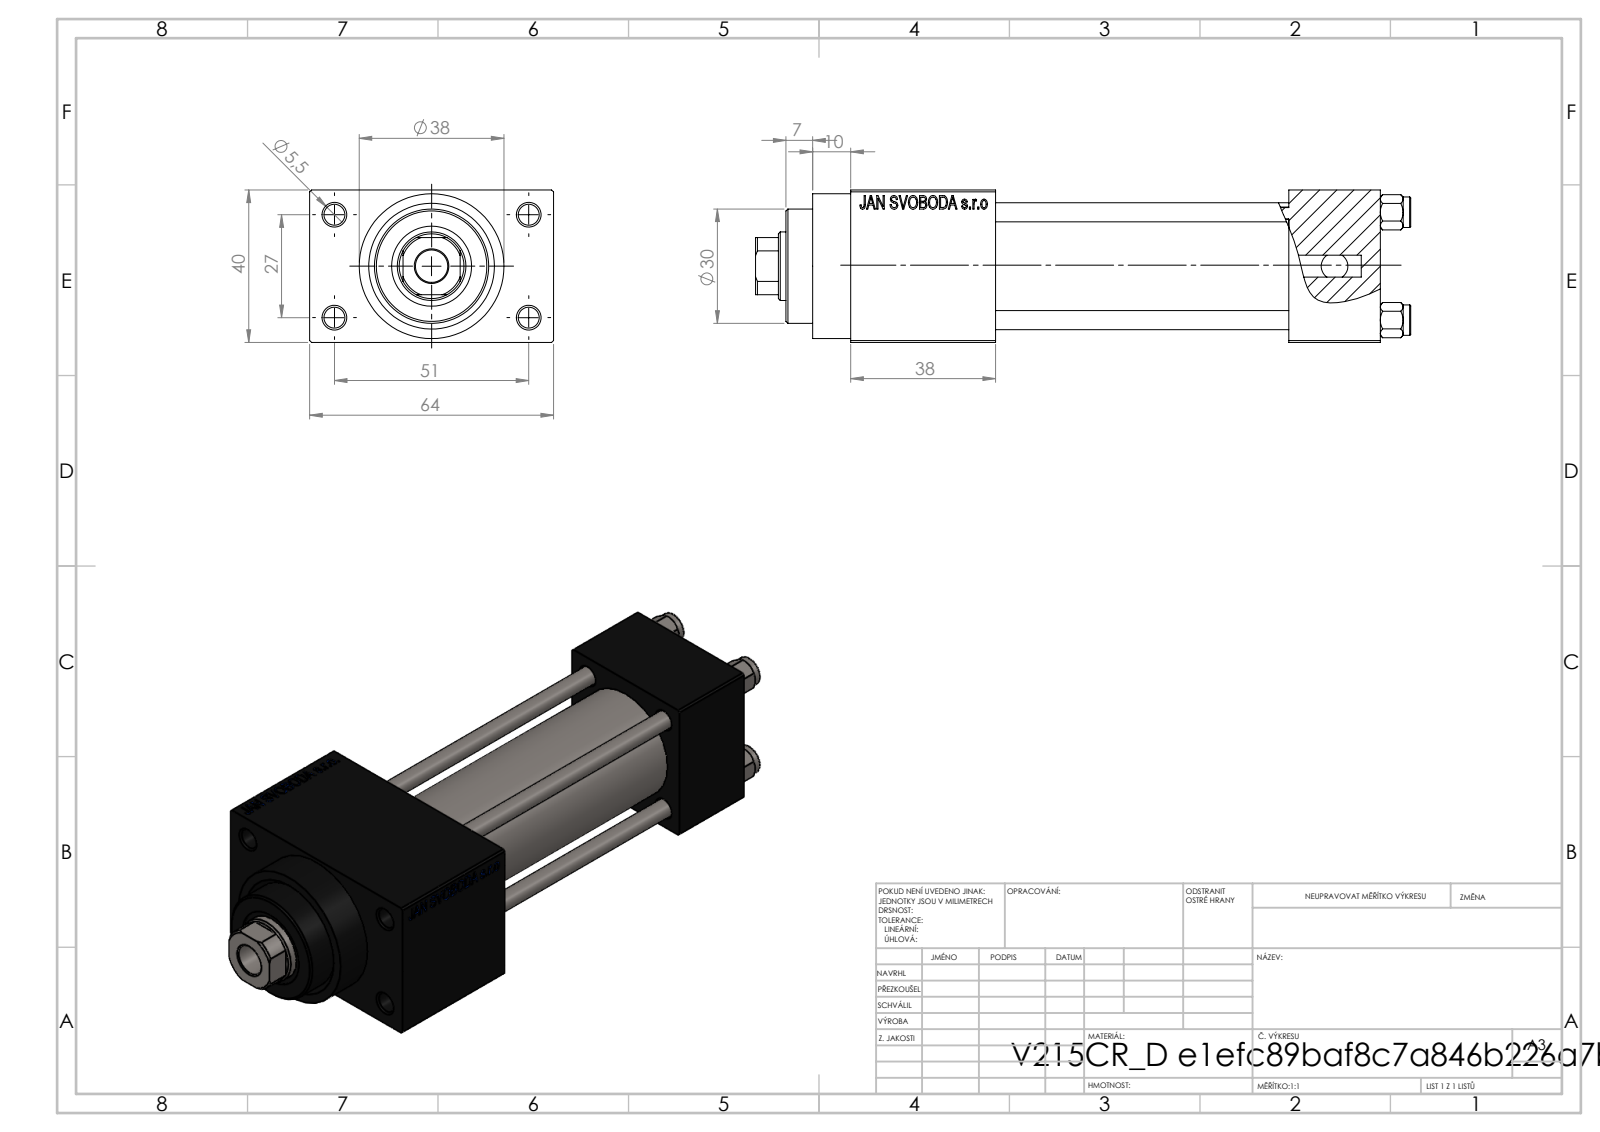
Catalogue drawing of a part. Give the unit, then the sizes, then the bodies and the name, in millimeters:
Units: millimetres
Overall size (bounding box): 172 × 64 × 40
Round holes (diameter × count): ⌀5 ×4, ⌀5.5 ×4, ⌀20 ×3, ⌀7 ×2, ⌀13.16 ×2, ⌀8.5 ×1, ⌀18 ×1, ⌀21 ×1, ⌀25 ×1, ⌀30 ×1
Round bosses / shafts (diameter × count): ⌀8 ×4, ⌀38 ×1, ⌀31 ×1
Partial cylindrical surfaces — rounded edges, fillets, slot ends (radius × count): R8.5 ×1
Main face-to-face distances: 40, 12, 77, 24, 101, 52, 38, 139, 115, 64
Hole centre spacings: 11.37, 20.01, 28.3, 28.85, 29.89, 39.66, 48.34, 27
Volume: 197 029 mm³ · Surface area: 73 489 mm²
Bodies: 11 solids, 1101 faces (495 planar, 86 cylindrical, 520 other)
Part name (STEP PRODUCT): V215_VC_A; V215CR_VCP_D; V215CR_D_Body; V215CR_D_TYCINKA (+1 more)
STEP written by: SolidWorks 2019 (CONFIG_CONTROL_DESIGN)
